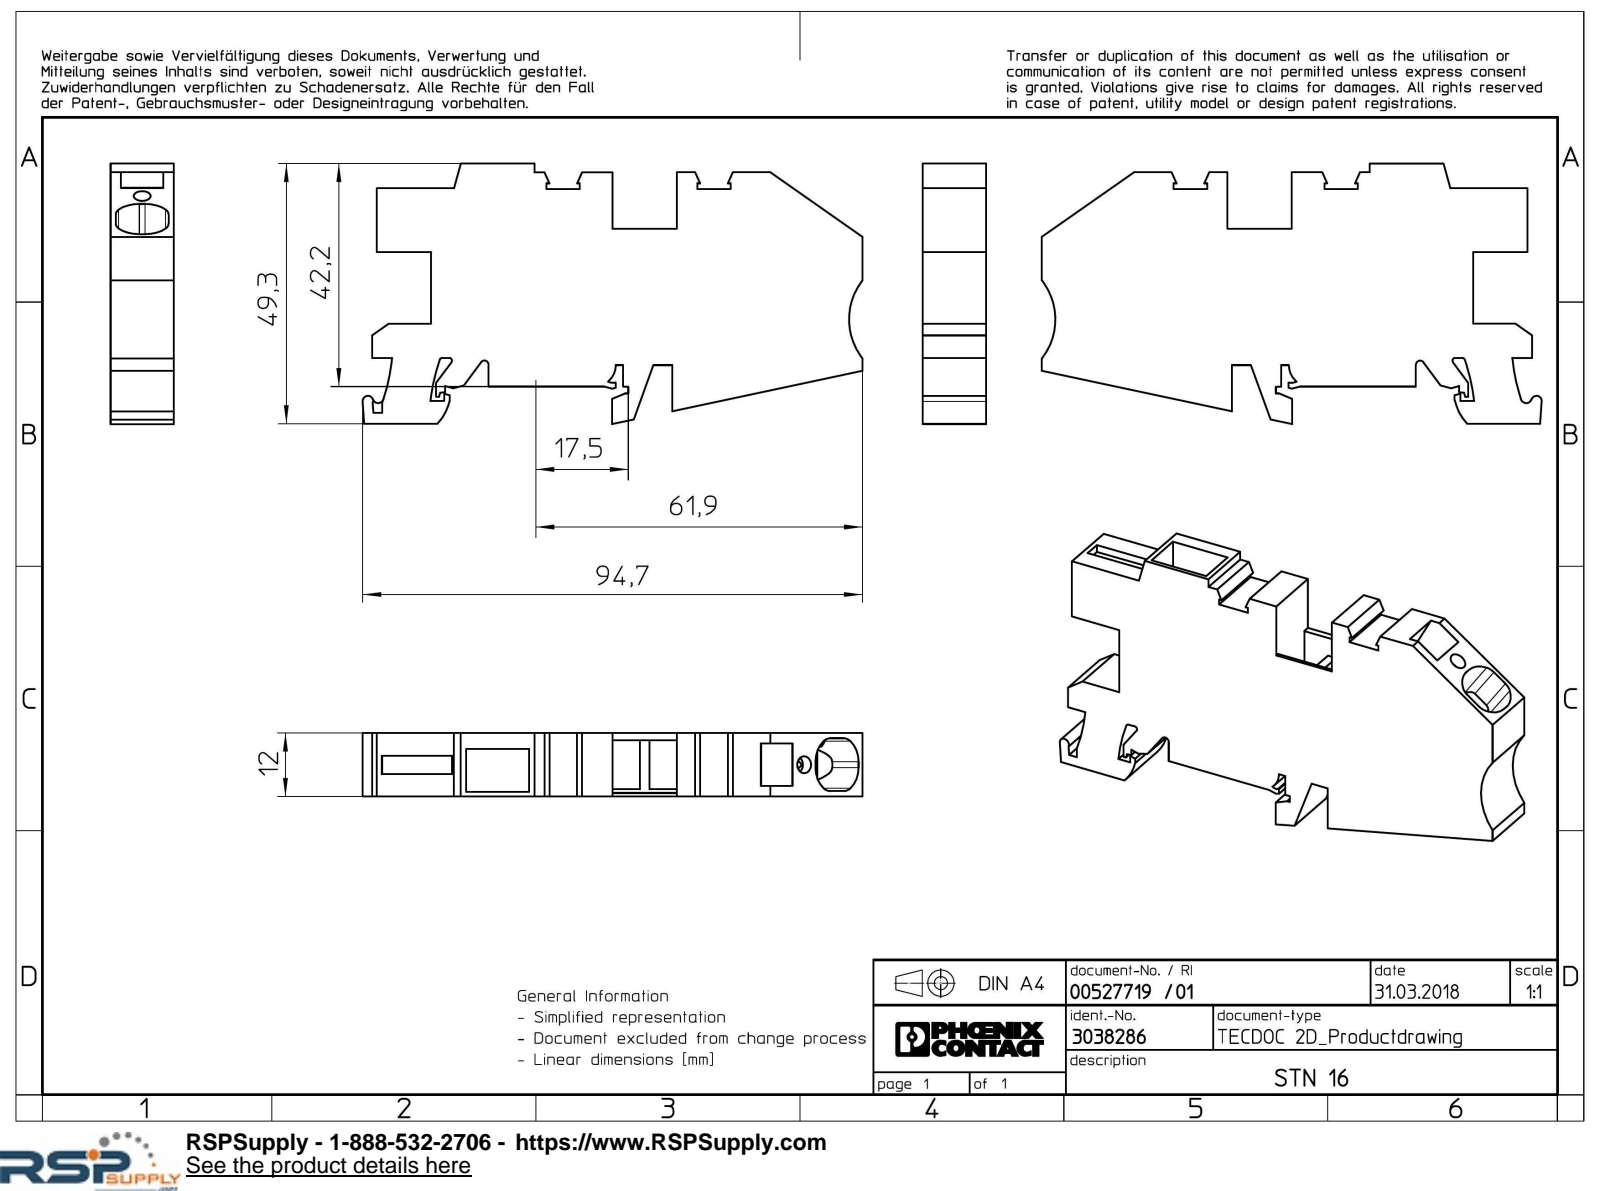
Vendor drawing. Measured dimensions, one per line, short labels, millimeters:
name: STN-16-Select
written by: Creo Elements/Direct Modeling 18.1I 14-Aug-2016 (C) Parametric Technology GmbH (AUTOMOTIVE_DESIGN)
unit: mm
bodies: 1 solid, 150 faces (123 planar, 25 cylindrical, 2 other)
size: 94.68 × 49.3 × 12
volume: 35 429 mm³; area: 14 193 mm²
holes: 1× ⌀3.2
rounds: 6× R0.5, 4× R2.5, 2× R5, 1× R0.8, 1× R1, 1× R1.04, 1× R1.6, 1× R4
face distances: 12, 5.2, 12.2, 7, 1.35, 1.8, 1.4, 10.6, 44.55, 7.05
